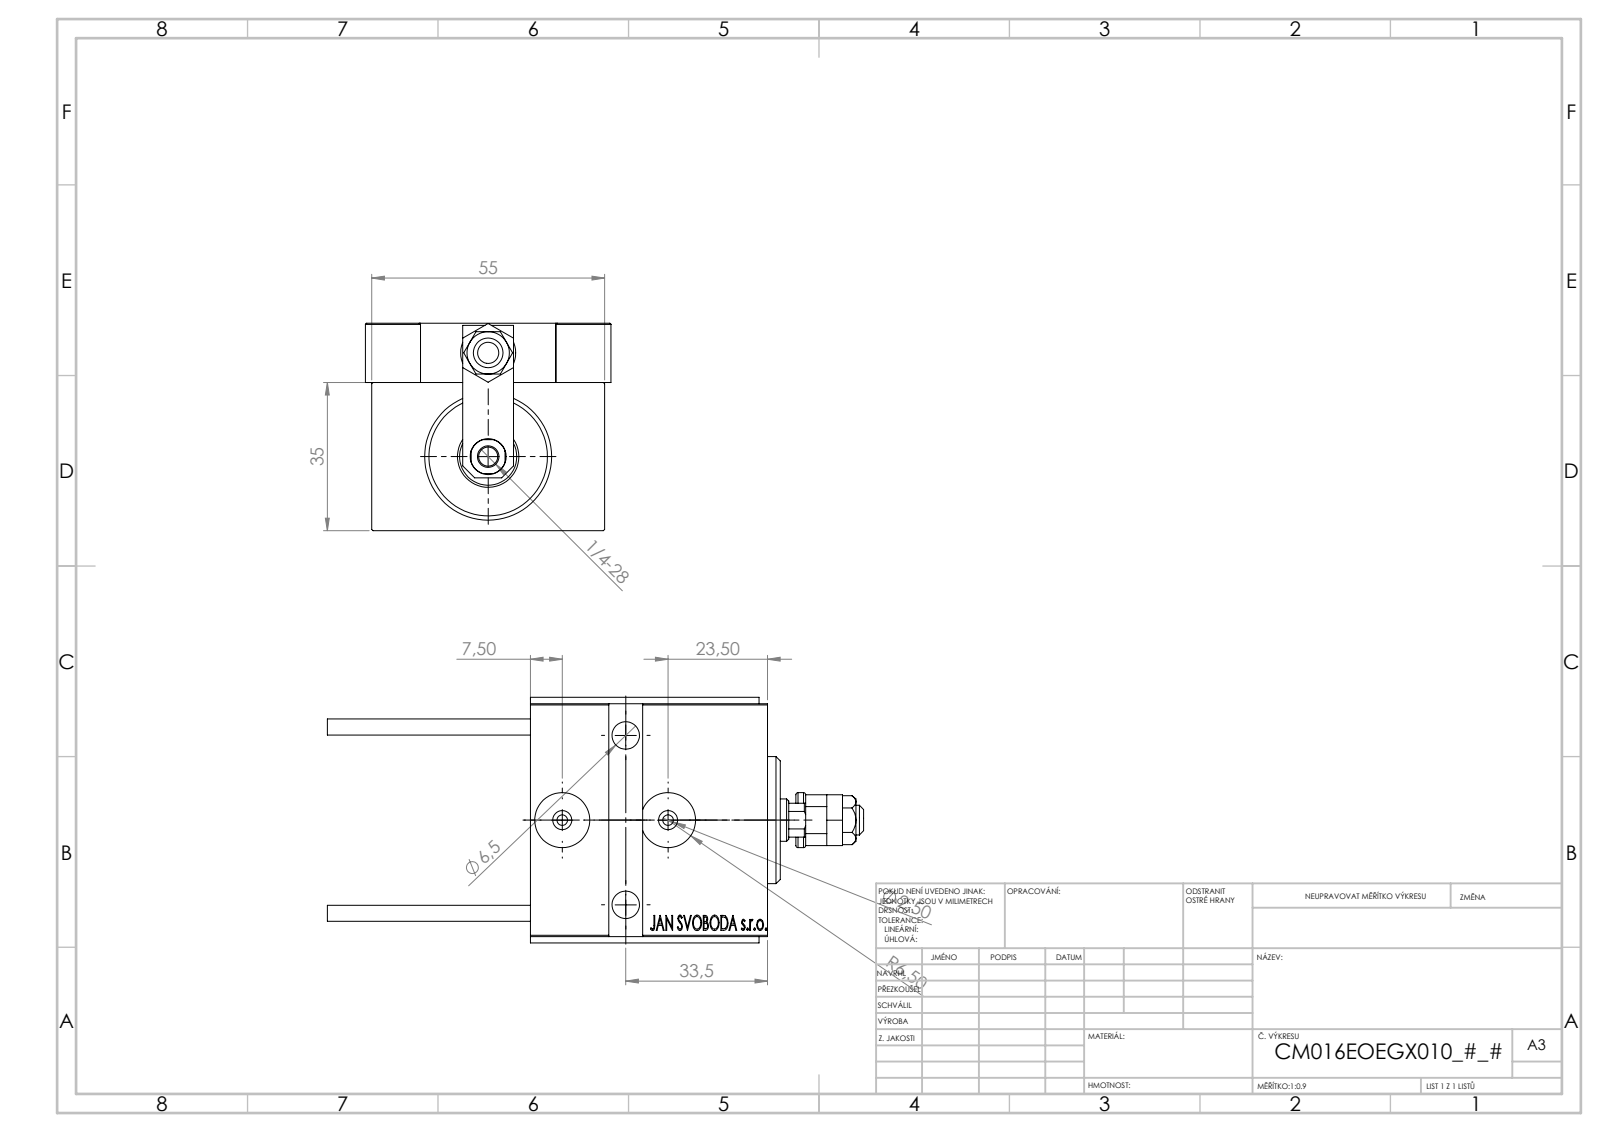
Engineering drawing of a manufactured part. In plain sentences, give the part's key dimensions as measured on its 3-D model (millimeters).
The part is named "Block; KONCOVKA; V450CM_E_VCP; ALLEN BOLT D8 (+8 more)". Its 3-D file was written by "SolidWorks 2019 (CONFIG_CONTROL_DESIGN)". It is 24 solids with 1289 faces: 571 planar, 177 cylindrical and 541 other. Overall it measures 126.7 by 58 by 49 millimeters. Its volume is 147 303 cubic millimeters and its surface area 46 186 square millimeters. Round holes: 5 of diameter 8, 4 of diameter 3.2, 4 of diameter 4, 2 of diameter 2.5, 2 of diameter 5, 2 of diameter 6.5, 2 of diameter 10.5, 2 of diameter 13, 1 of diameter 4.5, 1 of diameter 7, 1 of diameter 8.5, 1 of diameter 10. Round bosses or shafts: 2 of diameter 5, 2 of diameter 4.5, 2 of diameter 3.8, 1 of diameter 30, 1 of diameter 18, 1 of diameter 13, 1 of diameter 11. Partial cylindrical surfaces (rounded edges, fillets, slot ends): 26 of radius 0.3, 2 of radius 3, 1 of radius 4.5. The main face-to-face distances are 14, 49, 35, 55, 5, 10, 1.5, 3, 44, 7. The hole center spacings are 20.16, 25, 8.25, 10.31, 11.37, 19.29, 20, 22.36.
